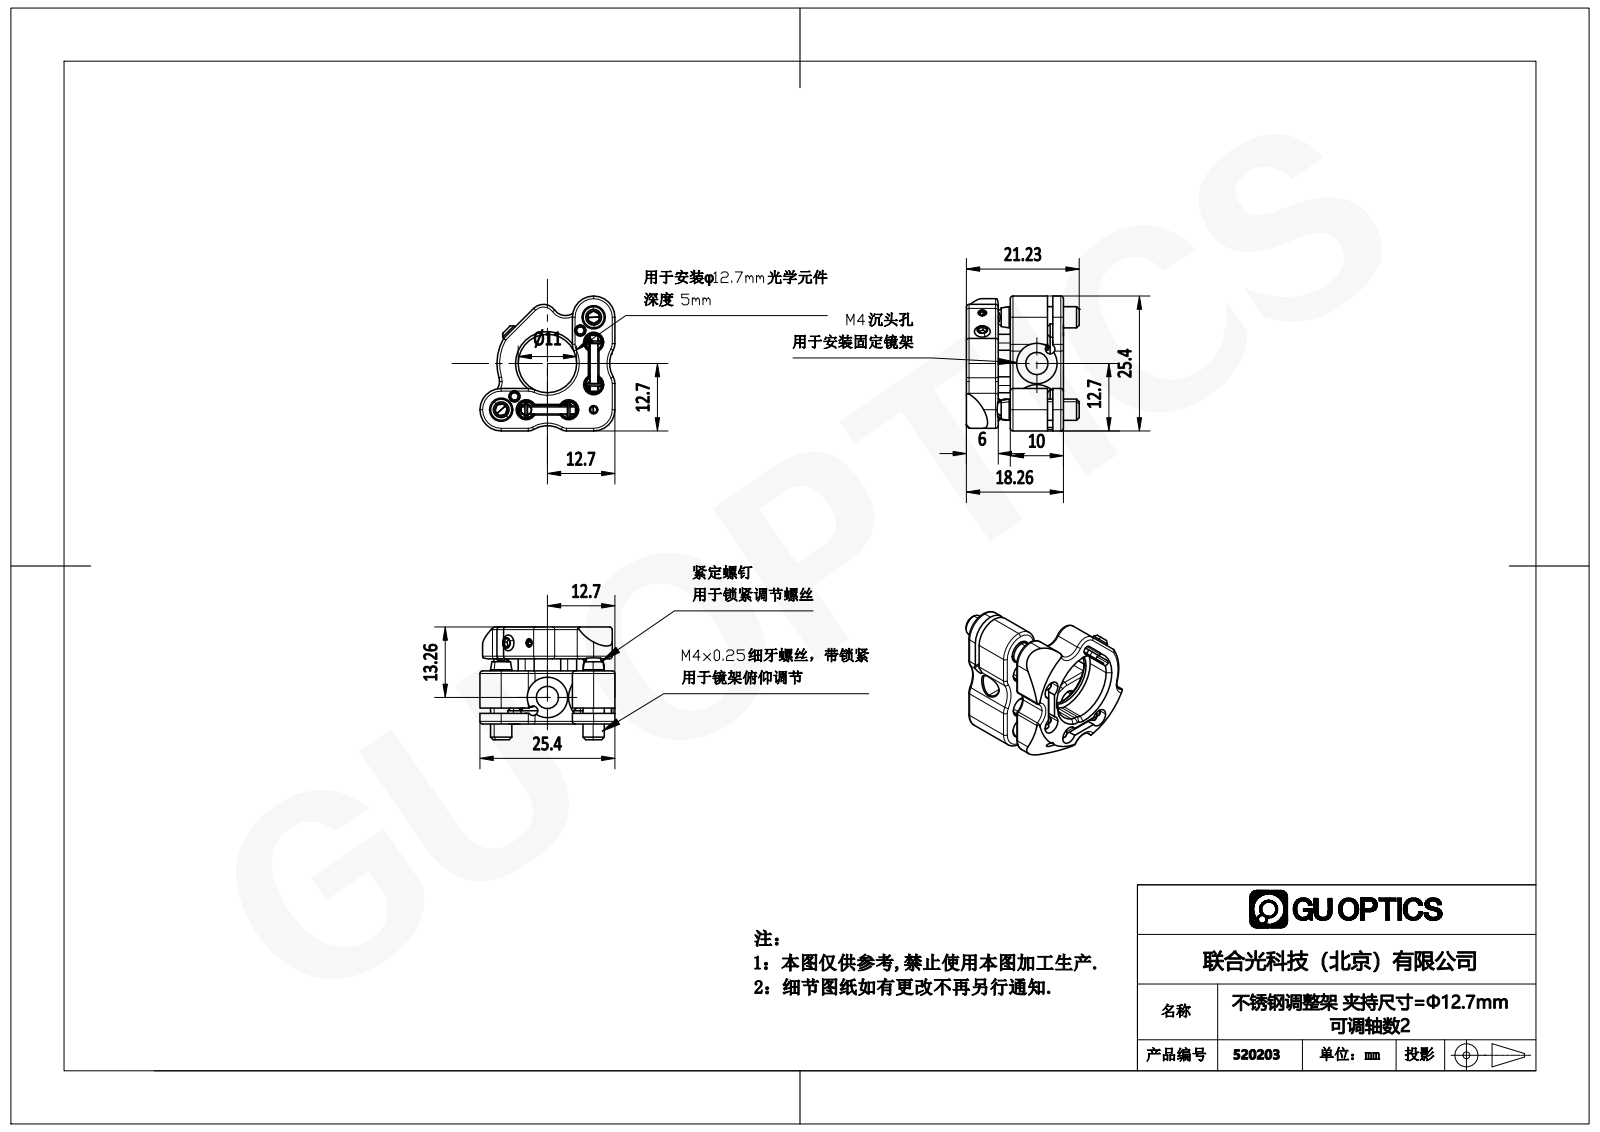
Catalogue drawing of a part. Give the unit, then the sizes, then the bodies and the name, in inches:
Units: inches
Overall size (bounding box): 1 × 1 × 0.836
Round holes (diameter × count): ⌀0.134 ×4, ⌀0.071 ×2, ⌀0.165 ×2, ⌀0.299 ×2, ⌀0.047 ×1, ⌀0.063 ×1, ⌀0.157 ×1, ⌀0.433 ×1
Round bosses / shafts (diameter × count): ⌀0.098 ×8, ⌀0.118 ×5, ⌀0.059 ×4, ⌀0.079 ×2, ⌀0.157 ×1
Partial cylindrical surfaces — rounded edges, fillets, slot ends (radius × count): R0.02 ×17, R0.098 ×6, R0.059 ×4, R0.138 ×3, R0.157 ×3, R0.031 ×2, R0.045 ×2, R0.079 ×2
Main face-to-face distances: 0.236, 0.089, 0.079, 0.315, 0.483, 0.394, 0.039, 0.404, 0.719, 0.325
Hole centre spacings: 0.377, 0.185, 0.5, 0.145, 0.315, 0.484, 0.533, 0.262
Bodies: 0 solids, 462 faces (101 planar, 169 cylindrical, 192 other)
STEP written by: SolidWorks 2018 (CONFIG_CONTROL_DESIGN)
